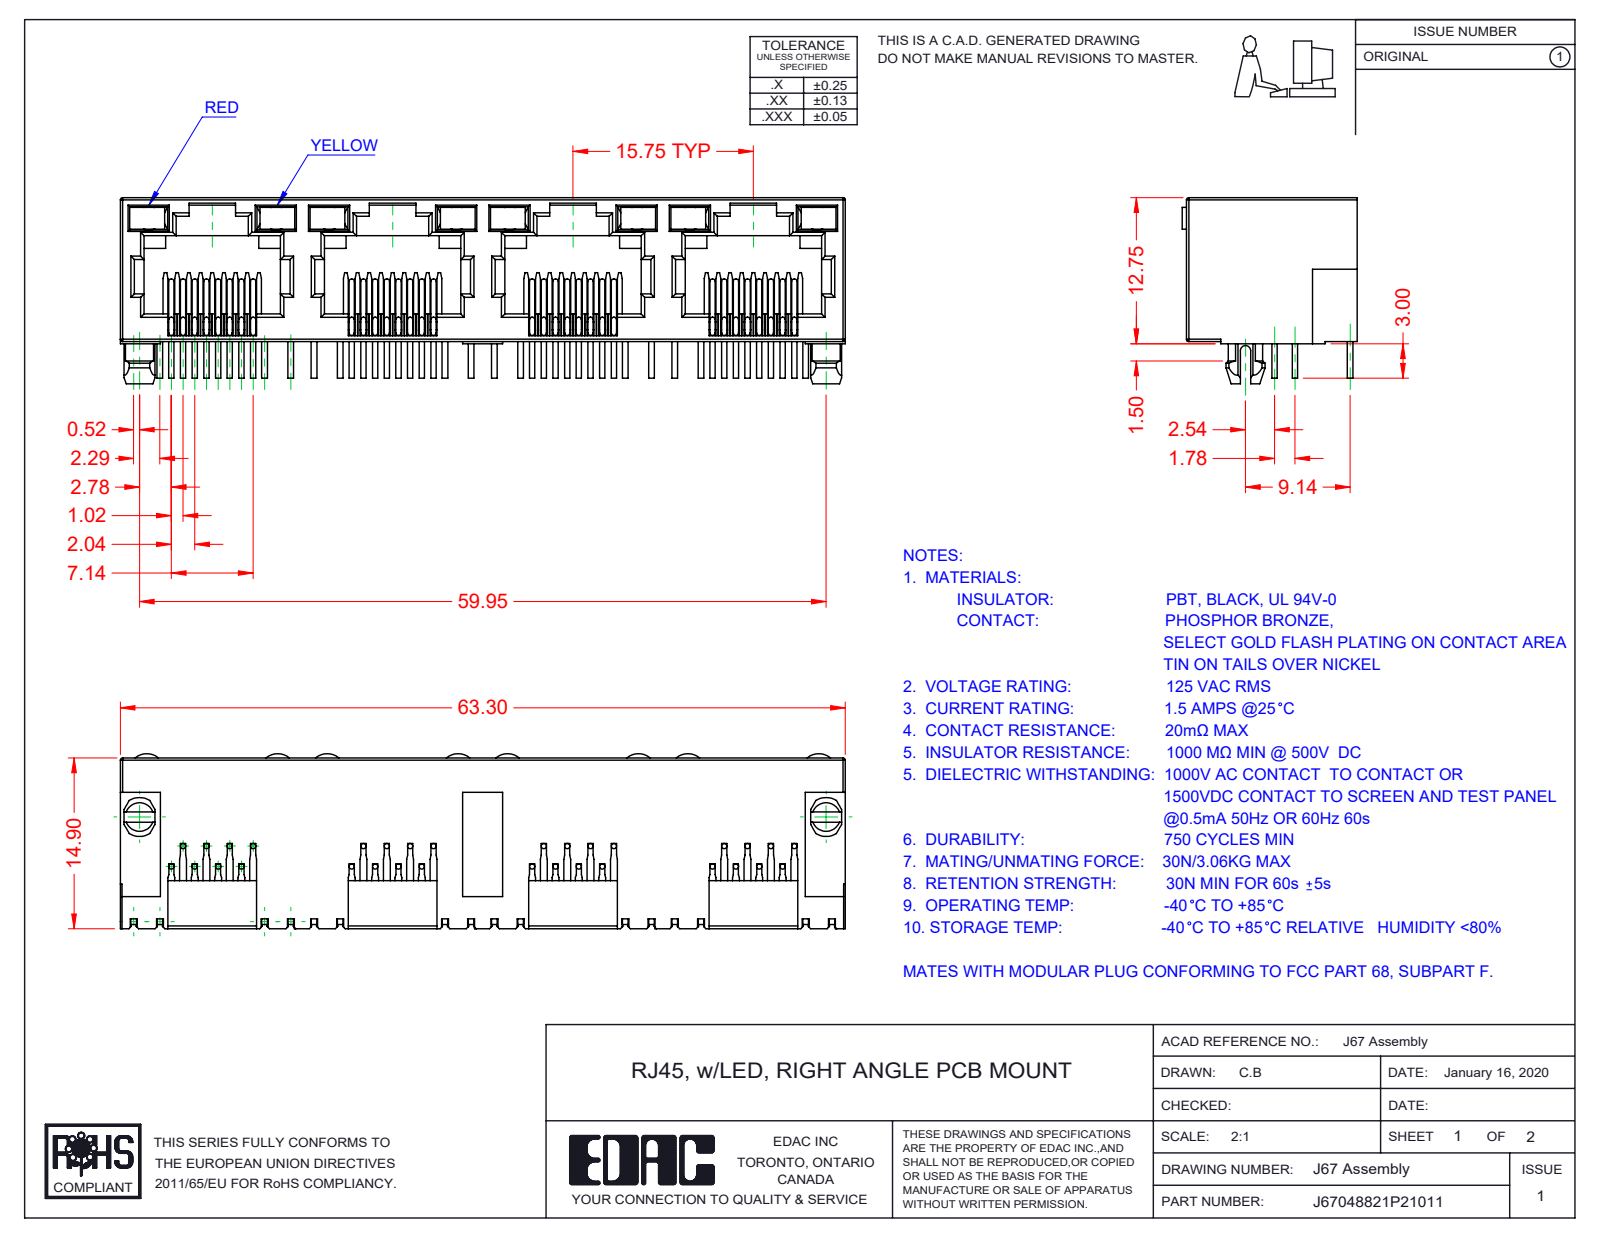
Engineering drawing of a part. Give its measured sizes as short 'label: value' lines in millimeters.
name: 67 LED LH_2-Red; 67 LED RH_1-Yellow; J67048822P21011; 67 Insulator (+1 more)
written by: SolidWorks 2016 (CONFIG_CONTROL_DESIGN)
unit: mm
bodies: 41 solids, 2465 faces (1781 planar, 476 cylindrical, 208 other)
size: 63.3 × 16.25 × 15.28
volume: 5 159 mm³; area: 11 573 mm²
bosses: 96× ⌀0.46
rounds: 66× R0.2, 29× R0.3, 9× R0.45, 8× R1.55, 2× R1.5, 2× R1.7, 1× R0.35, 1× R1
face distances: 0.5, 12.55, 1.89, 0.89, 10, 15.75, 1, 1.39, 11, 11.89
